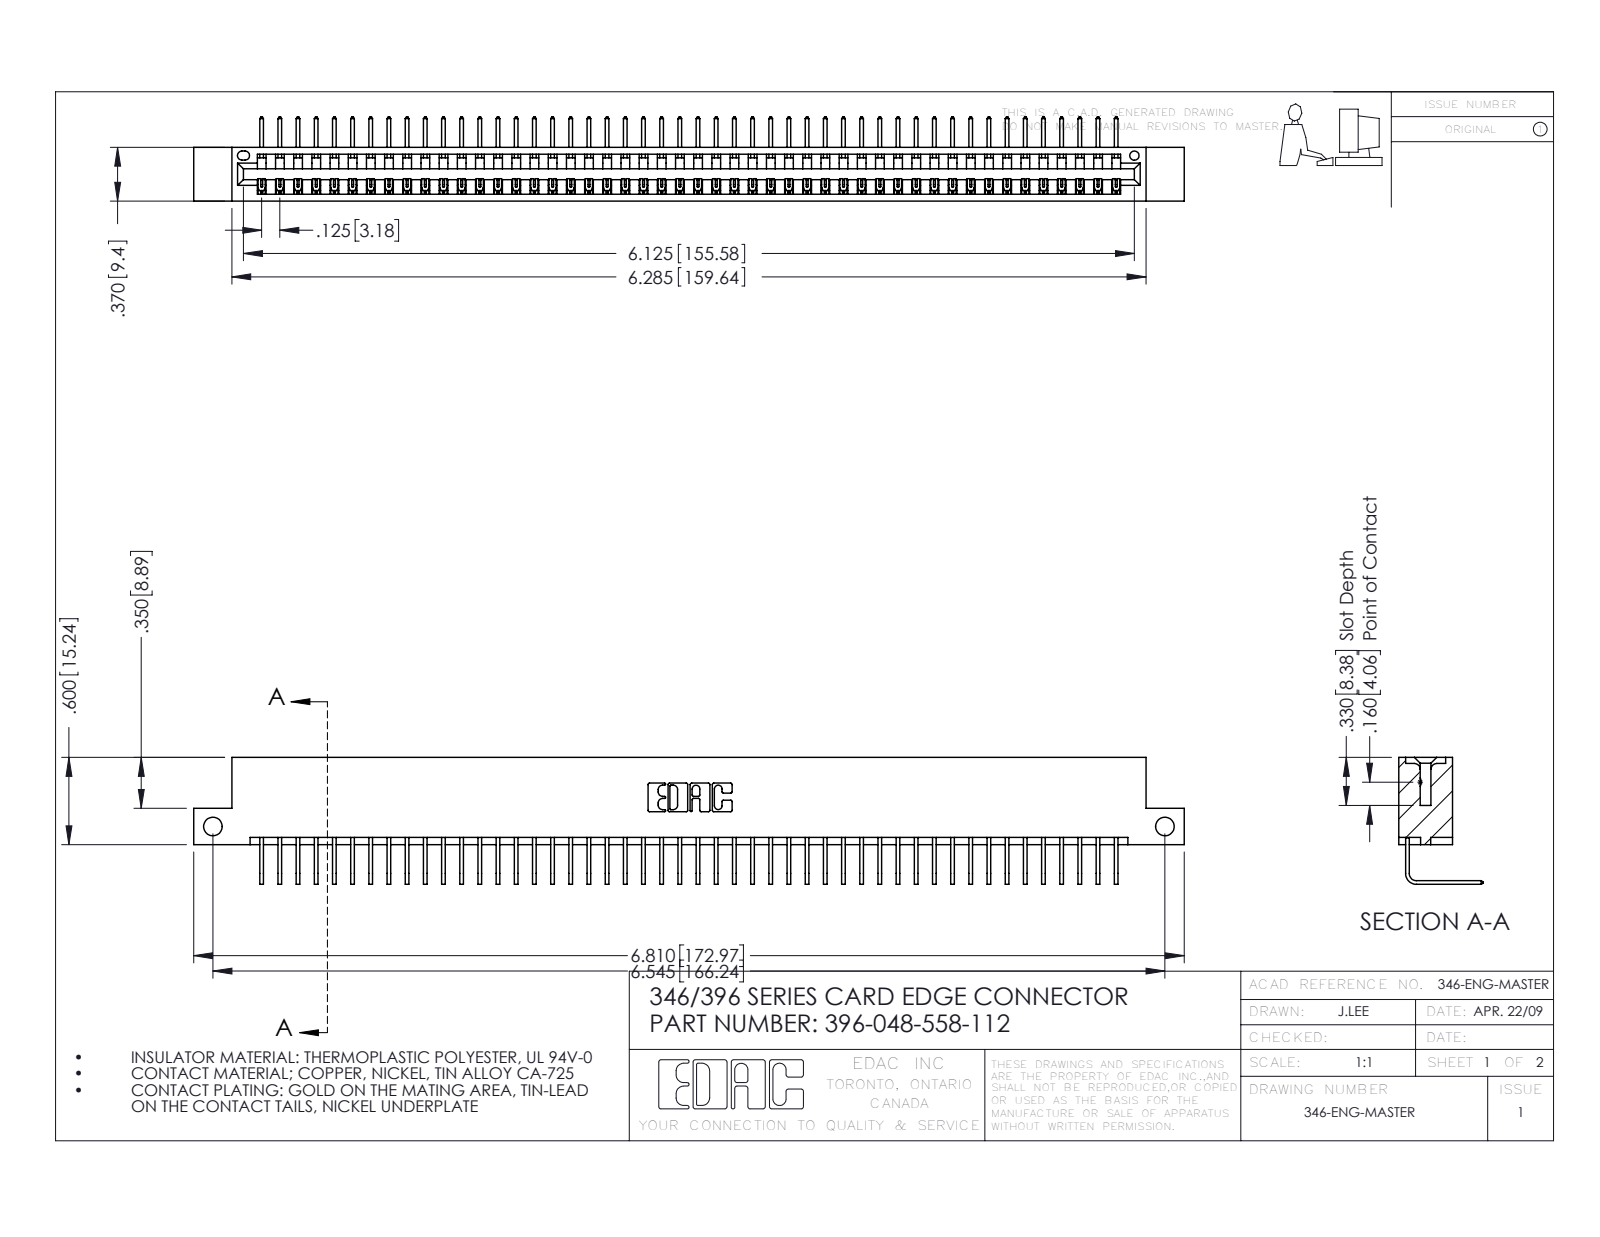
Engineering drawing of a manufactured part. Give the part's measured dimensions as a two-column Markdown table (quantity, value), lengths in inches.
| quantity | value |
| --- | --- |
| part name | 396-048-558-112; 345-292-001_558 Tail - 2; 346 Part_Flush Mounting Lugs - Side Mount |
| STEP written by | SolidWorks 2016 (CONFIG_CONTROL_DESIGN) |
| units | inches |
| bodies | 49 solids, 3002 faces (2092 planar, 910 cylindrical, 0 other) |
| overall size | 6.81 × 0.873 × 0.58 |
| volume | 1.017 in³ |
| surface area | 33.65 in² |
| round holes (diameter × count) | 0.128 × 2, 0.064 × 1 |
| partial cylindrical surfaces (radius × count) | 0.006 × 96, 0.01 × 22, 0.007 × 6, 0.031 × 6, 0.026 × 3, 0.031 × 2, 0.04 × 2, 0.014 × 1 |
| main face-to-face distances | 0.322, 0.048, 0.37, 0.25, 0.298, 0.025, 0.072, 0.148, 0.222, 0.1 |
| hole center spacings | 6.545 |
